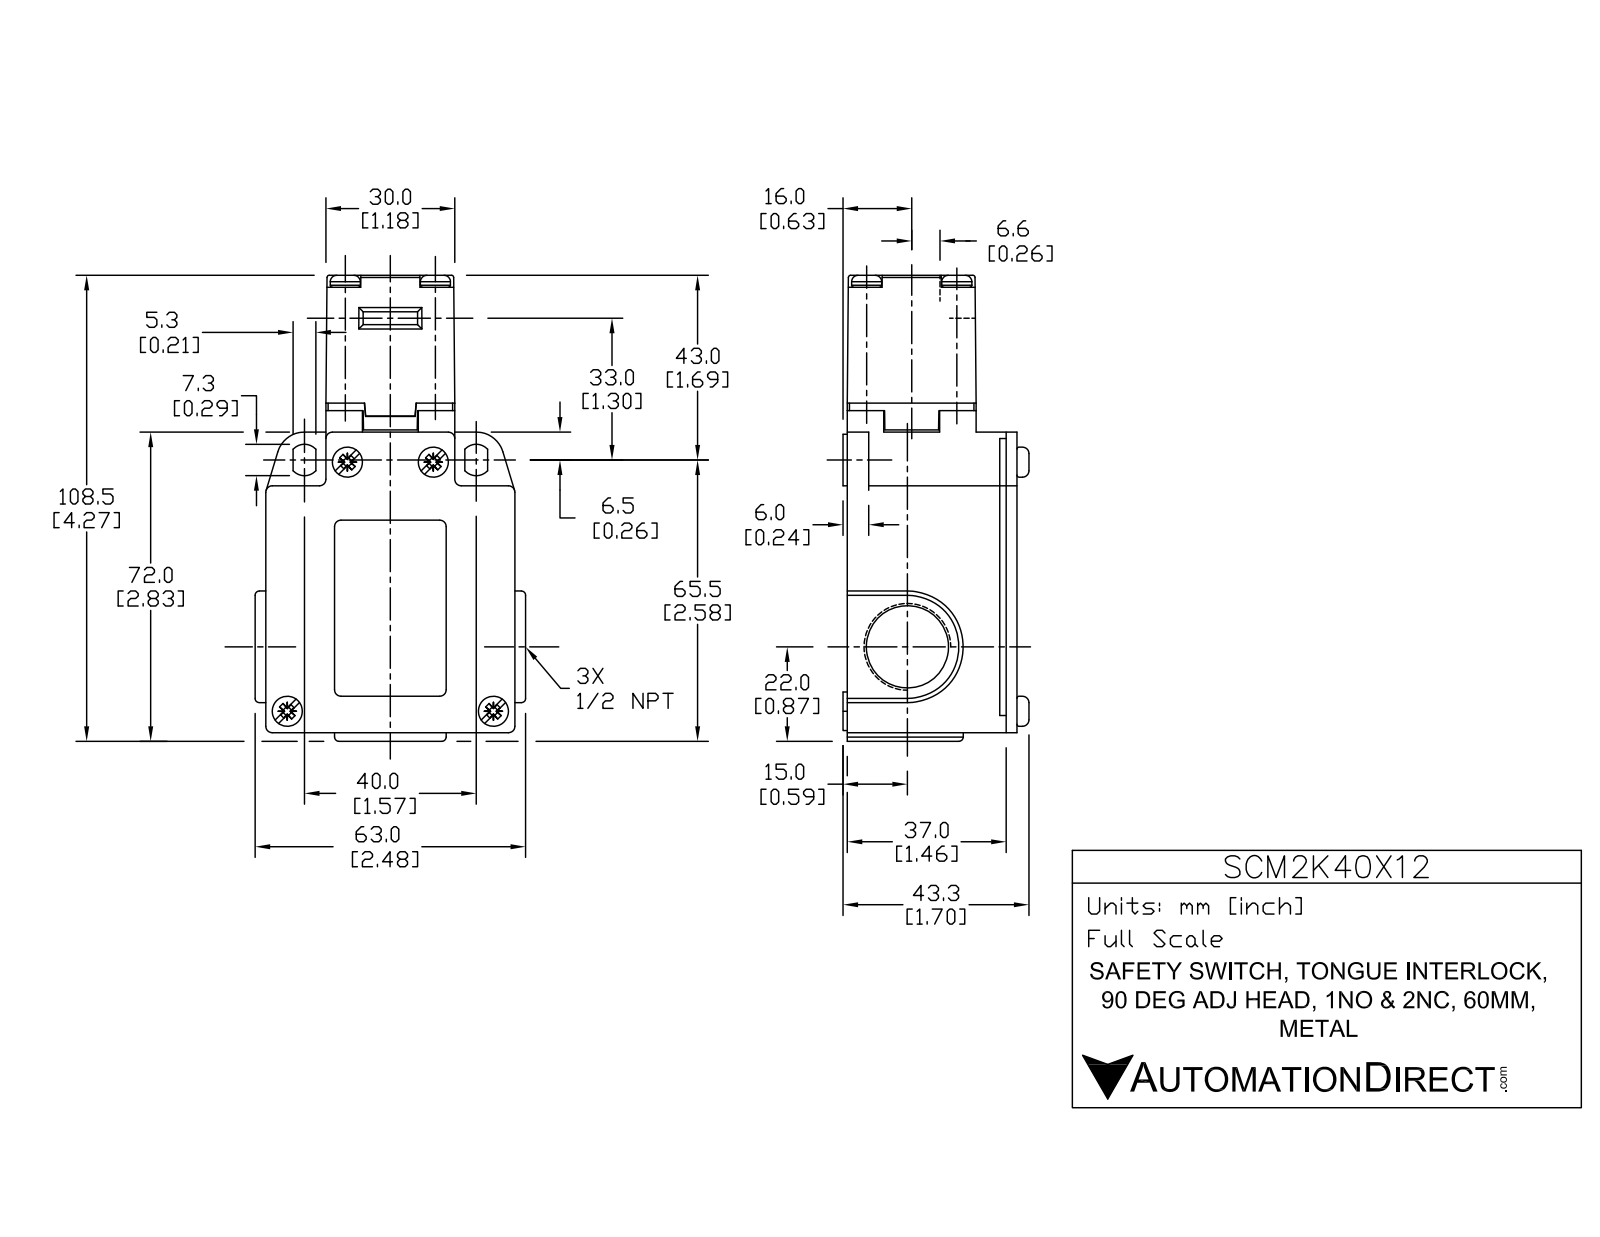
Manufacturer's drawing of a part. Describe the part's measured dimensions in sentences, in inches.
The part is named "SCM2K40X12". Its 3-D file was written by "SolidWorks 2017 (AUTOMOTIVE_DESIGN)". It is 2 solids with 206 faces: 106 planar, 78 cylindrical and 22 other. Overall it measures 4.272 by 2.441 by 1.705 inches. Its volume is 10.84 cubic inches and its surface area 43.53 square inches. Round holes: 2 of diameter 0.276, 2 of diameter 0.669, 2 of diameter 0.748. Round bosses or shafts: 6 of diameter 0.276, 2 of diameter 0.472, 2 of diameter 0.354. Partial cylindrical surfaces (rounded edges, fillets, slot ends): 12 of radius 0.059, 4 of radius 0.02, 2 of radius 0.144, 2 of radius 0.256, 2 of radius 0.512, 1 of radius 0.453, 1 of radius 0.472. The main face-to-face distances are 1.555, 1.732, 0.551, 1.181, 2.283, 0.079, 0.236, 0.374, 2.756, 0.118. The hole center spacings are 0.557, 0.827.
